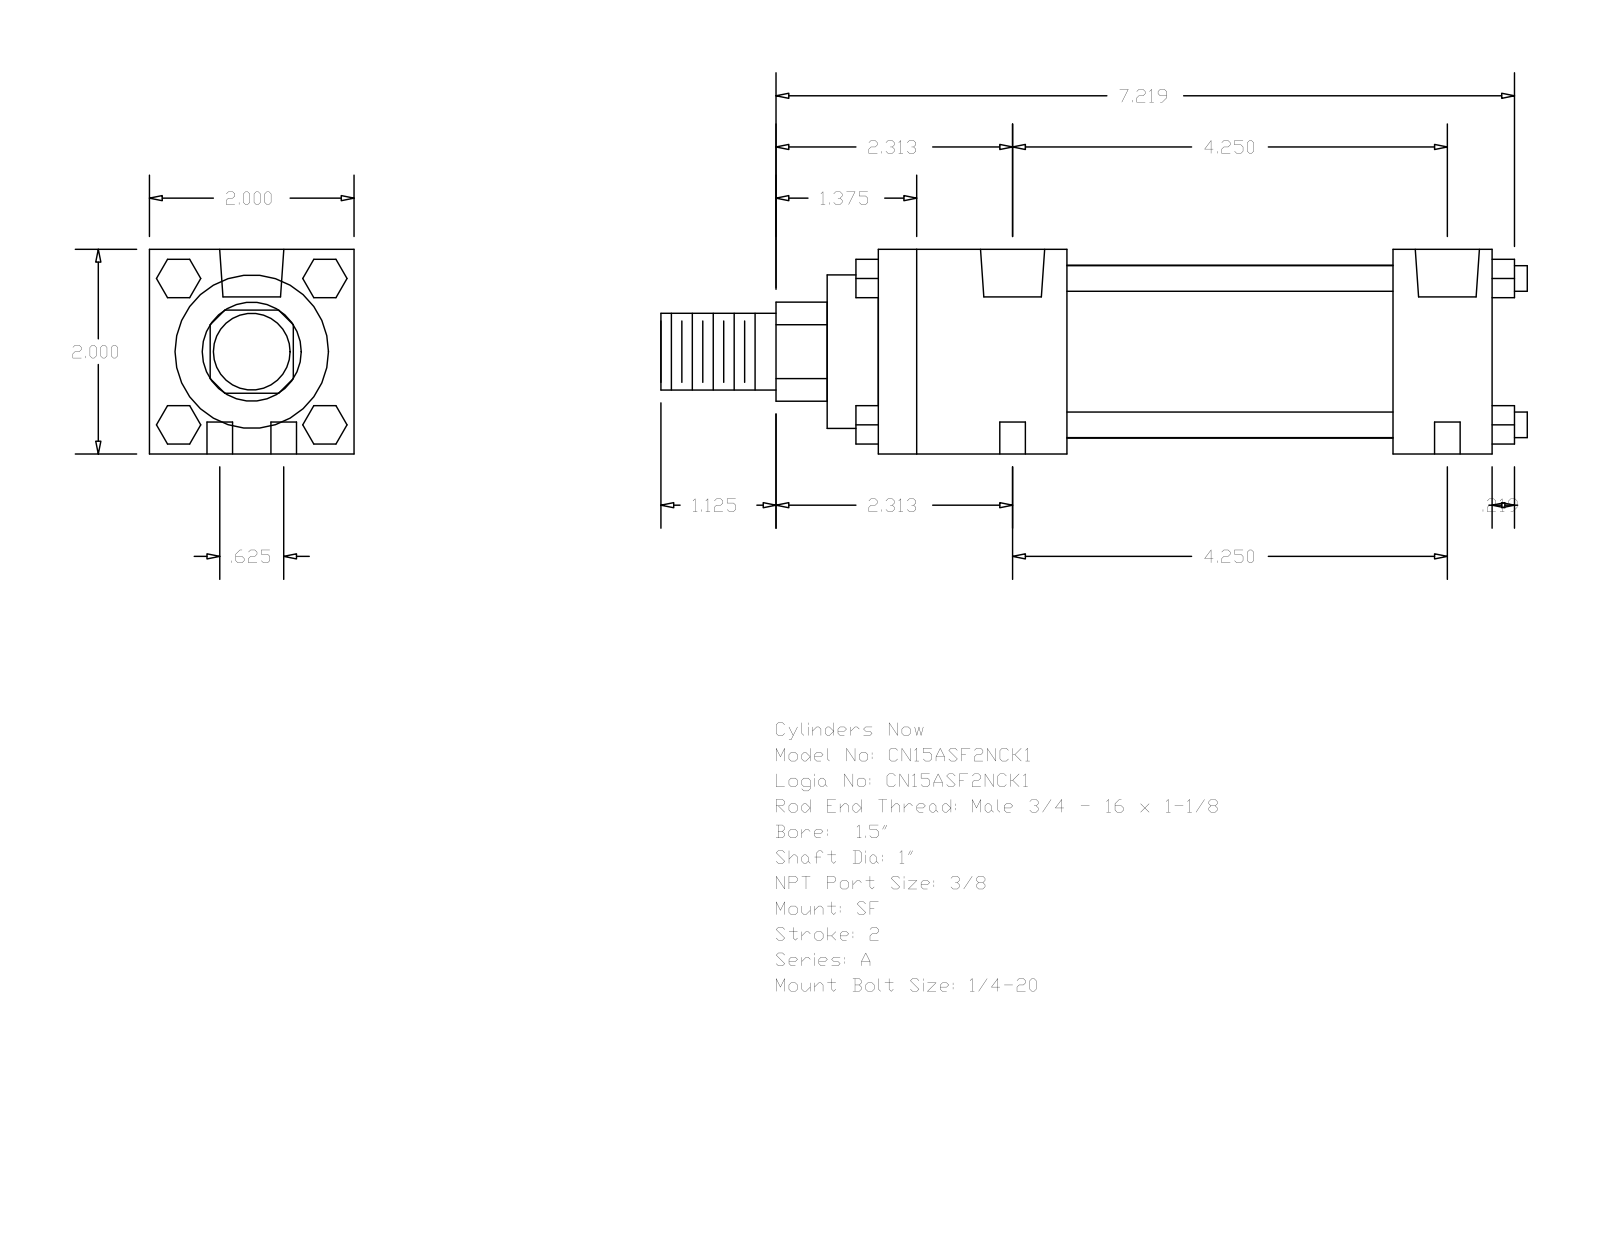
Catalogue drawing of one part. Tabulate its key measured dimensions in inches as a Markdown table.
| quantity | value |
| --- | --- |
| part name | A_SF__0150_1 |
| STEP written by | GSSL Pune (CONFIG_CONTROL_DESIGN) |
| units | inches |
| bodies | 0 solids, 124 faces (94 planar, 30 cylindrical, 0 other) |
| overall size | 8.469 × 2 × 2 |
| round holes (diameter × count) | 0.25 × 4, 0.219 × 2, 0.627 × 2 |
| round bosses / shafts (diameter × count) | 0.25 × 4, 1.69 × 1, 1.5 × 1, 1 × 1, 0.75 × 1 |
| partial cylindrical surfaces (radius × count) | 0.484 × 1 |
| main face-to-face distances | 2, 6, 1.844, 5.031, 3.187, 4.156, 0.969, 0.5, 2.344, 5.531 |
| hole center spacings | 0.313, 4.261, 4.25, 0.625, 4.296, 3.937 |
